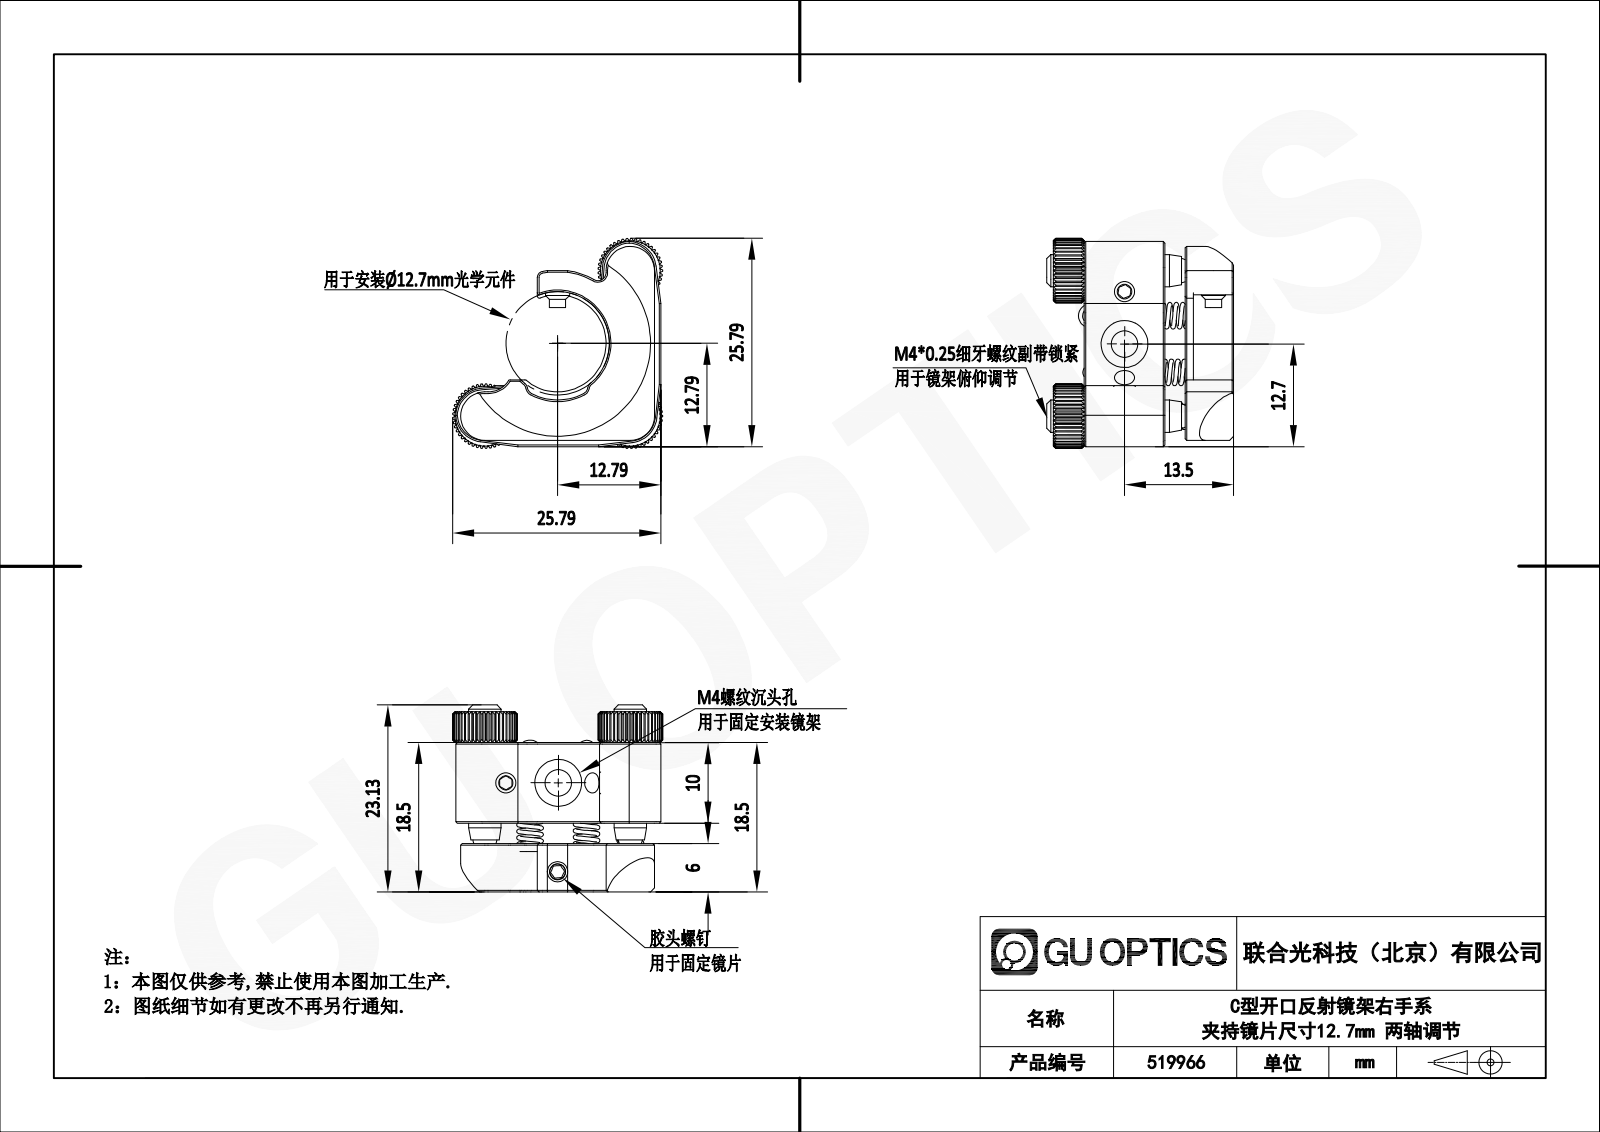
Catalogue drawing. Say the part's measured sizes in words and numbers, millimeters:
Its 3-D file was written by "SolidWorks 2021 (CONFIG_CONTROL_DESIGN)". It is 0 solids with 810 faces: 305 planar, 198 cylindrical and 307 other. Overall it measures 26 by 26 by 23.13 millimeters. Round holes: 5 of diameter 5.8, 4 of diameter 2.8, 4 of diameter 3.2, 2 of diameter 1.5, 2 of diameter 2.5, 2 of diameter 3.3, 1 of diameter 4.6, 1 of diameter 5.5. Round bosses or shafts: 5 of diameter 1.5, 2 of diameter 4, 1 of diameter 3, 1 of diameter 2. Partial cylindrical surfaces (rounded edges, fillets, slot ends): 10 of radius 0.75, 6 of radius 3, 5 of radius 0.25, 5 of radius 1, 5 of radius 3.5, 4 of radius 0.9, 2 of radius 4, 2 of radius 6. The main face-to-face distances are 10, 2.4, 12.4, 6, 8.4, 18.4, 0.79, 22.2, 16.2, 13.8. The hole center spacings are 3.4, 5.41, 5.59, 7, 12.41, 12.59, 13.54, 18.
